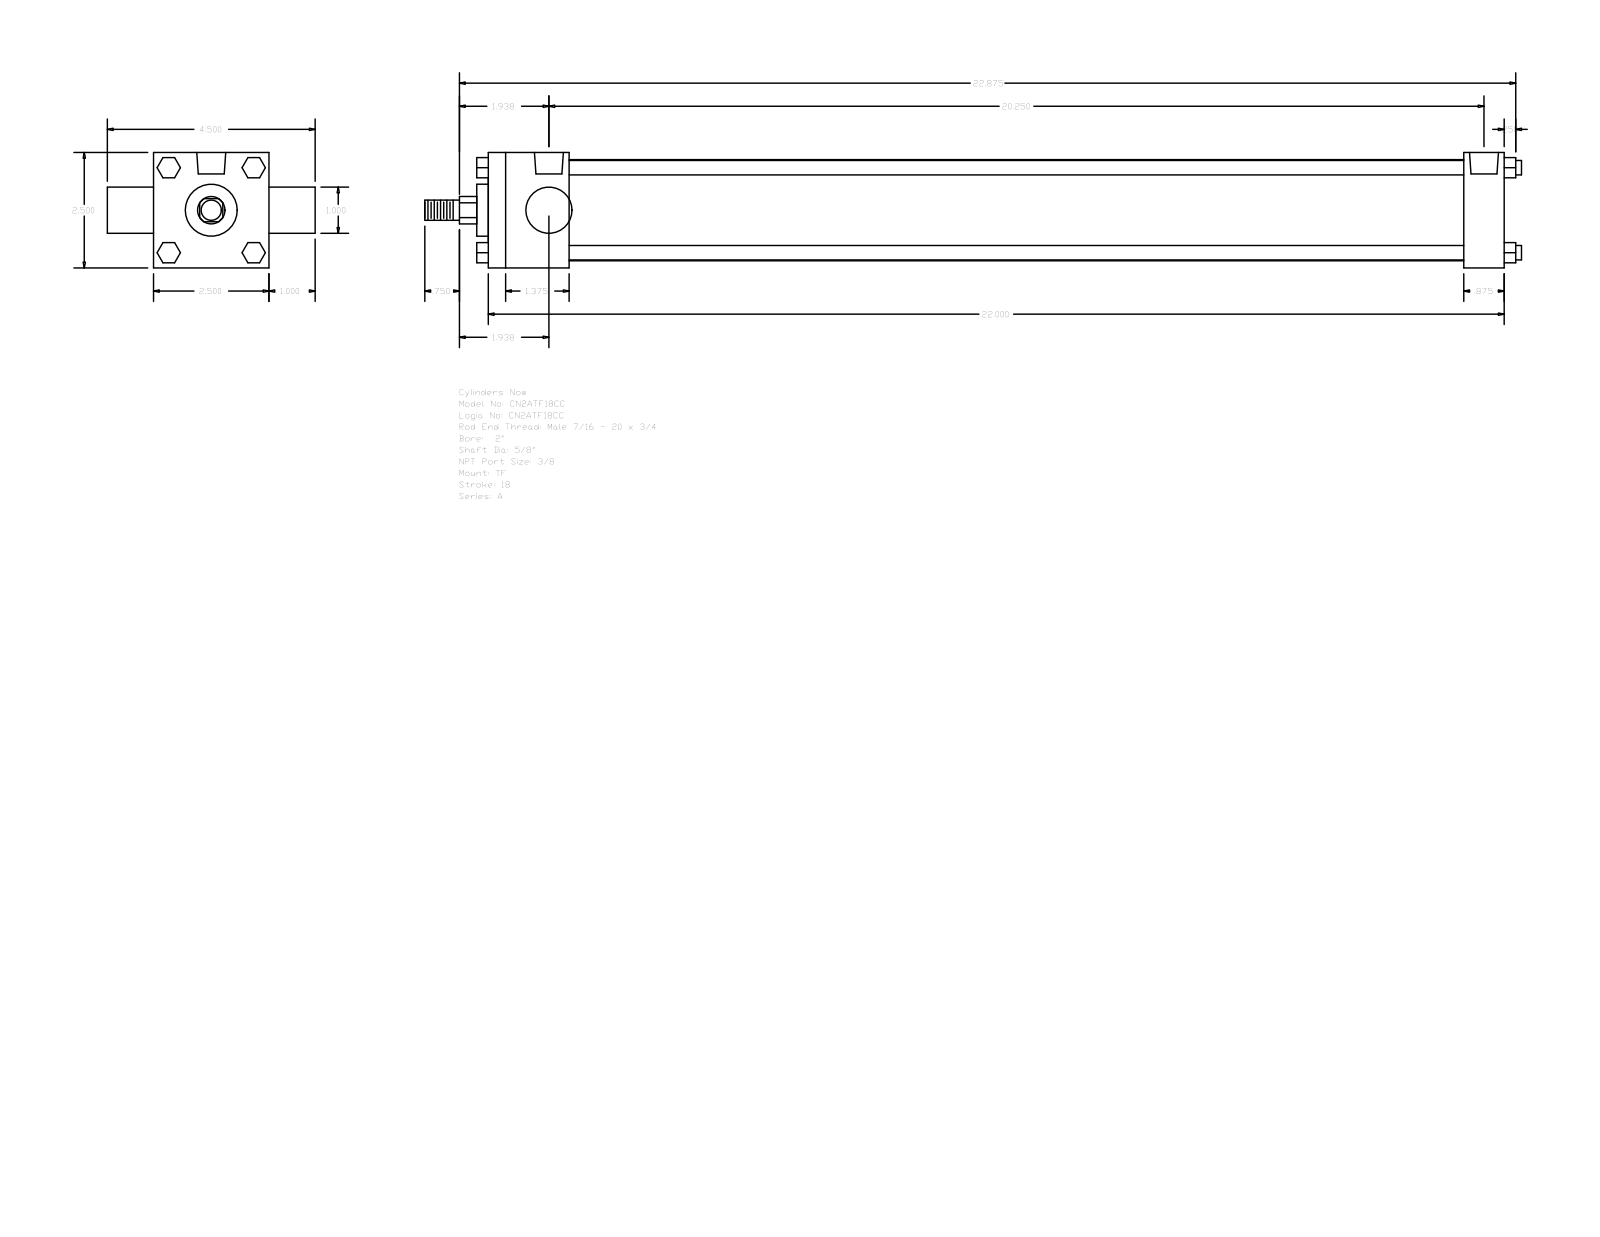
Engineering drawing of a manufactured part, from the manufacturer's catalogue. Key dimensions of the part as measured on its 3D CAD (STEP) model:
Part name (STEP PRODUCT): A_TF__0200_0.625
STEP written by: GSSL Pune (CONFIG_CONTROL_DESIGN)
Units: millimetres
Bodies: 0 solids, 120 faces (92 planar, 28 cylindrical, 0 other)
Overall size (bounding box): 603.25 × 114.3 × 63.5
Round holes (diameter × count): ⌀5.56 ×3, ⌀15.93 ×2
Round bosses / shafts (diameter × count): ⌀7.94 ×4, ⌀55.63 ×1, ⌀28.57 ×1, ⌀25.4 ×1, ⌀15.88 ×1, ⌀11.11 ×1
Partial cylindrical surfaces — rounded edges, fillets, slot ends (radius × count): R7.54 ×1
Main face-to-face distances: 63.5, 558.79, 44.45, 536.57, 492.12, 514.34, 22.22, 25.4, 88.9, 6.35
Hole centre spacings: 3.97, 3.98, 506.4, 510.37, 510.38, 514.35
